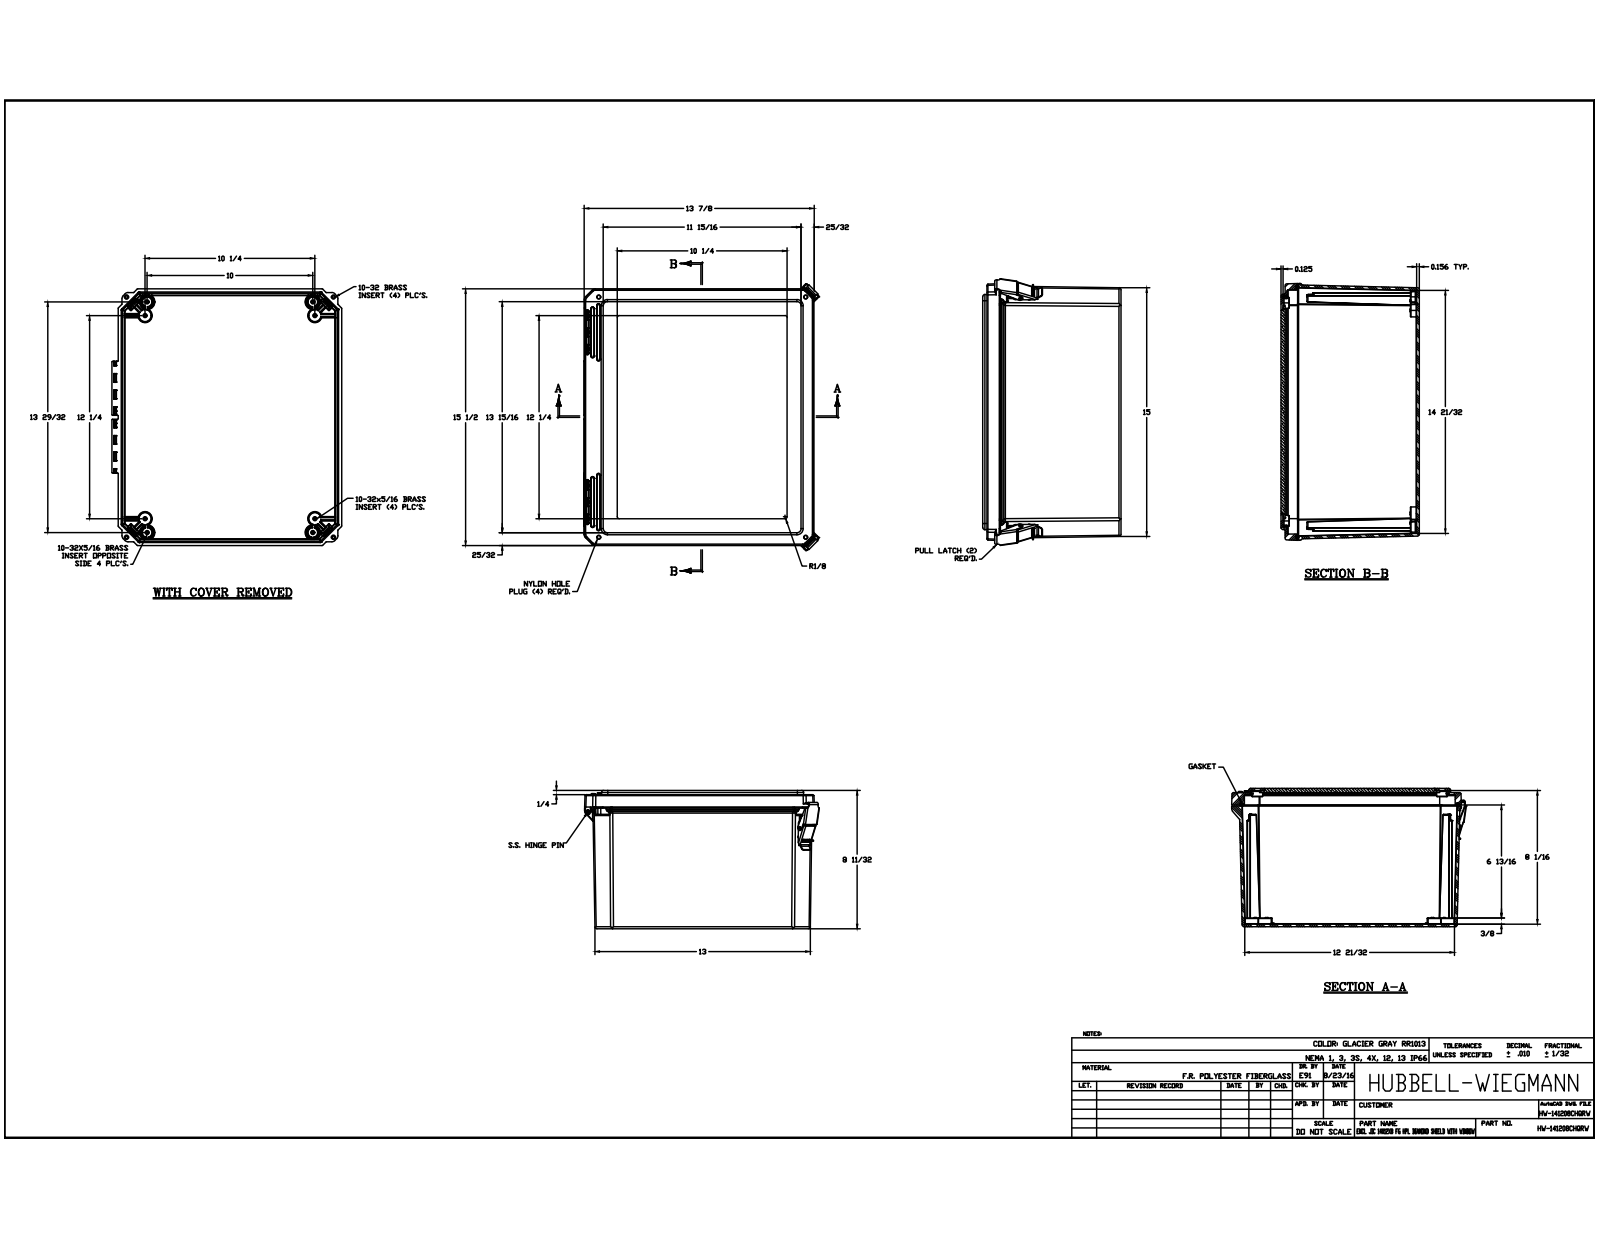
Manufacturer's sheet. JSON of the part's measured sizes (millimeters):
{"part_name": "HW-141208CHQRW; DS141208BOX; BRASS INSERT-(; BRASS INSERT-(_1 (+8 more)", "step_written_by": "Autodesk Inventor 2017 (AUTOMOTIVE_DESIGN)", "units": "millimeters", "bodies": {"solids": 34, "faces": 2323, "planar": 835, "cylindrical": 920, "other": 568}, "overall_size": [411.52, 361.27, 211.87], "volume_mm3": 2603000, "surface_area_mm2": 1220000, "round_holes": [[3.96, 16], [3.43, 9], [3.86, 8], [3.81, 4], [6.4, 4], [6.43, 4], [3.43, 2], [5.56, 2], [5.77, 2], [7.94, 2], [9.52, 2], [3.48, 1]], "round_bosses_or_shafts": [[6.25, 16], [7.62, 4], [5.3, 4], [11.05, 2], [3.43, 1]], "partial_cylinders_radius": [[0.25, 175], [0.13, 88], [0.76, 63], [0.51, 49], [1.52, 34], [1.59, 28], [2.29, 26], [3.17, 26]], "face_to_face_distances": [3.96, 4.07, 207.91, 211.87, 4.03, 206.16, 202.2, 5.71, 3.17, 6.35], "hole_center_spacings": [6.35, 40.23, 258.01, 290.19, 21.02, 32.54, 285.71, 285.72]}
